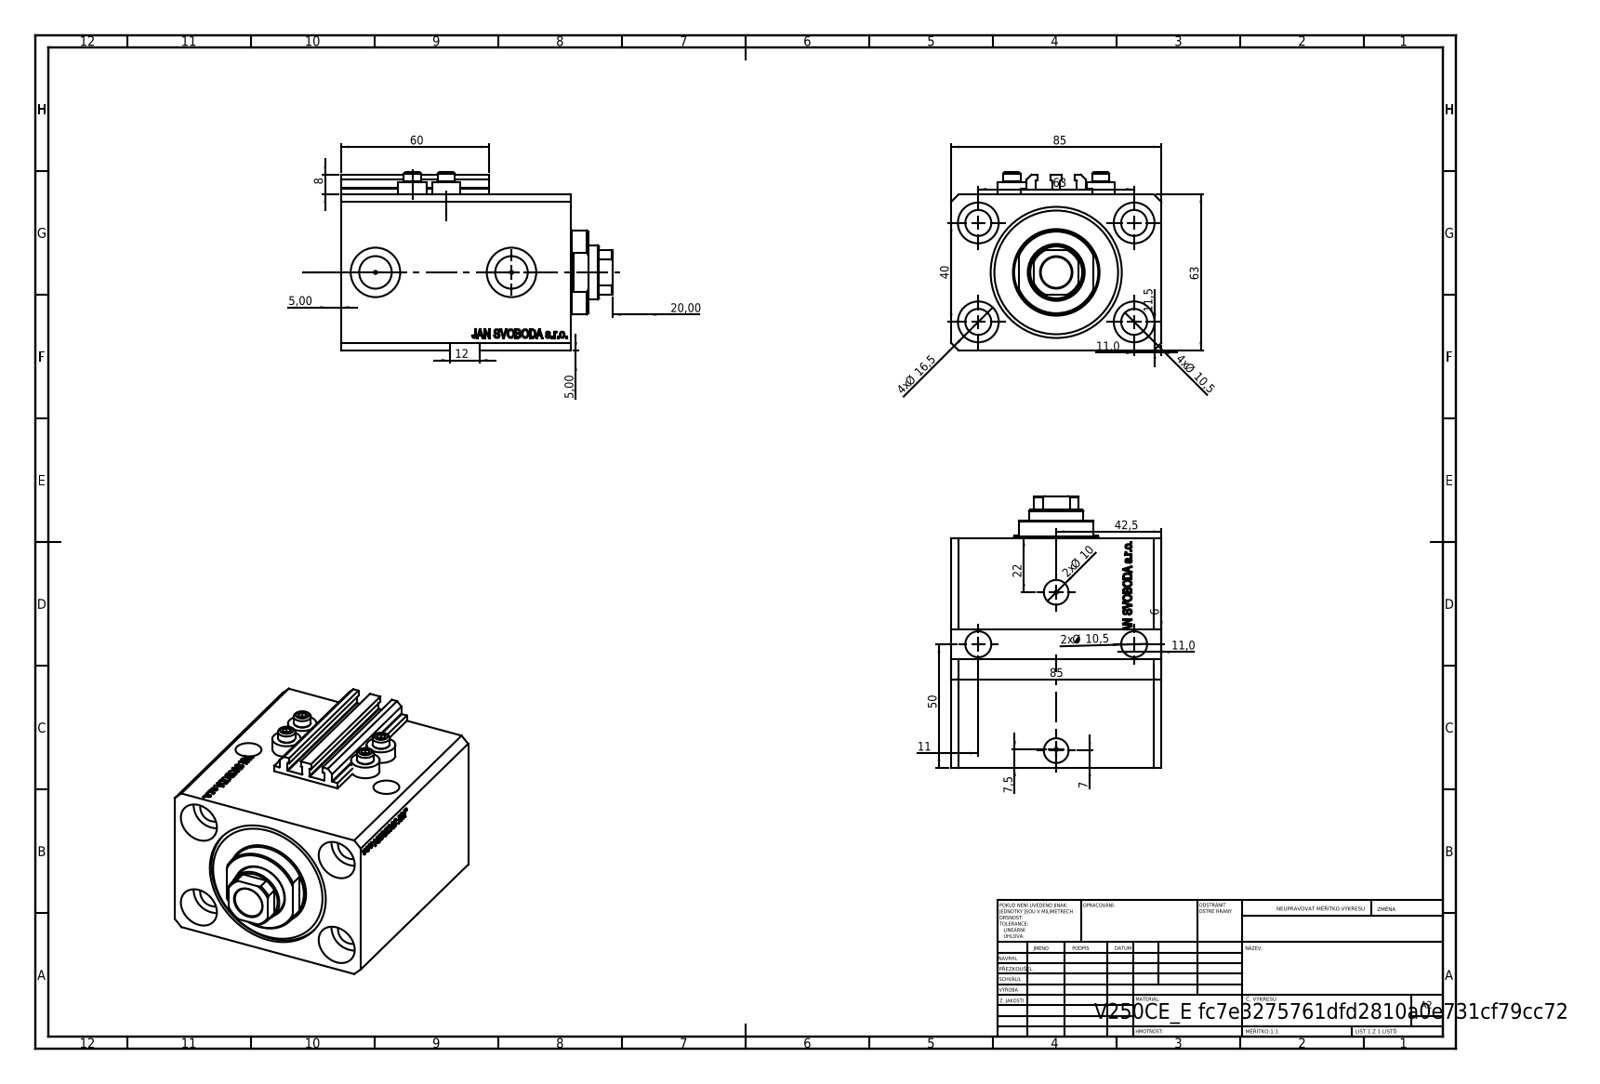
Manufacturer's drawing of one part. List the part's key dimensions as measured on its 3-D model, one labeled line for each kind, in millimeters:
Part name (STEP PRODUCT): V250CE_E_Body; V250CE_C_VCP; ALLEN BOLT V250CE; V250CE_VC_E
STEP written by: SolidWorks 2019 (CONFIG_CONTROL_DESIGN)
Units: millimetres
Bodies: 8 solids, 1087 faces (535 planar, 126 cylindrical, 426 other)
Overall size (bounding box): 109.9 × 85 × 72
Volume: 437 230 mm³ · Surface area: 97 950 mm²
Round holes (diameter × count): ⌀10.5 ×6, ⌀1.25 ×4, ⌀4 ×4, ⌀16.5 ×4, ⌀10 ×2, ⌀13.16 ×2, ⌀20 ×2, ⌀12.5 ×1, ⌀22 ×1, ⌀40 ×1, ⌀53 ×1
Round bosses / shafts (diameter × count): ⌀11.6 ×4, ⌀7 ×4, ⌀34 ×1
Partial cylindrical surfaces — rounded edges, fillets, slot ends (radius × count): R0.2 ×10, R10.5 ×1
Main face-to-face distances: 63, 85, 93, 65.9, 54.5, 27.1, 11.4, 81.6, 3, 65
Hole centre spacings: 37.31, 63, 13.6, 15.4, 24.96, 28.02, 28.43, 33.62
